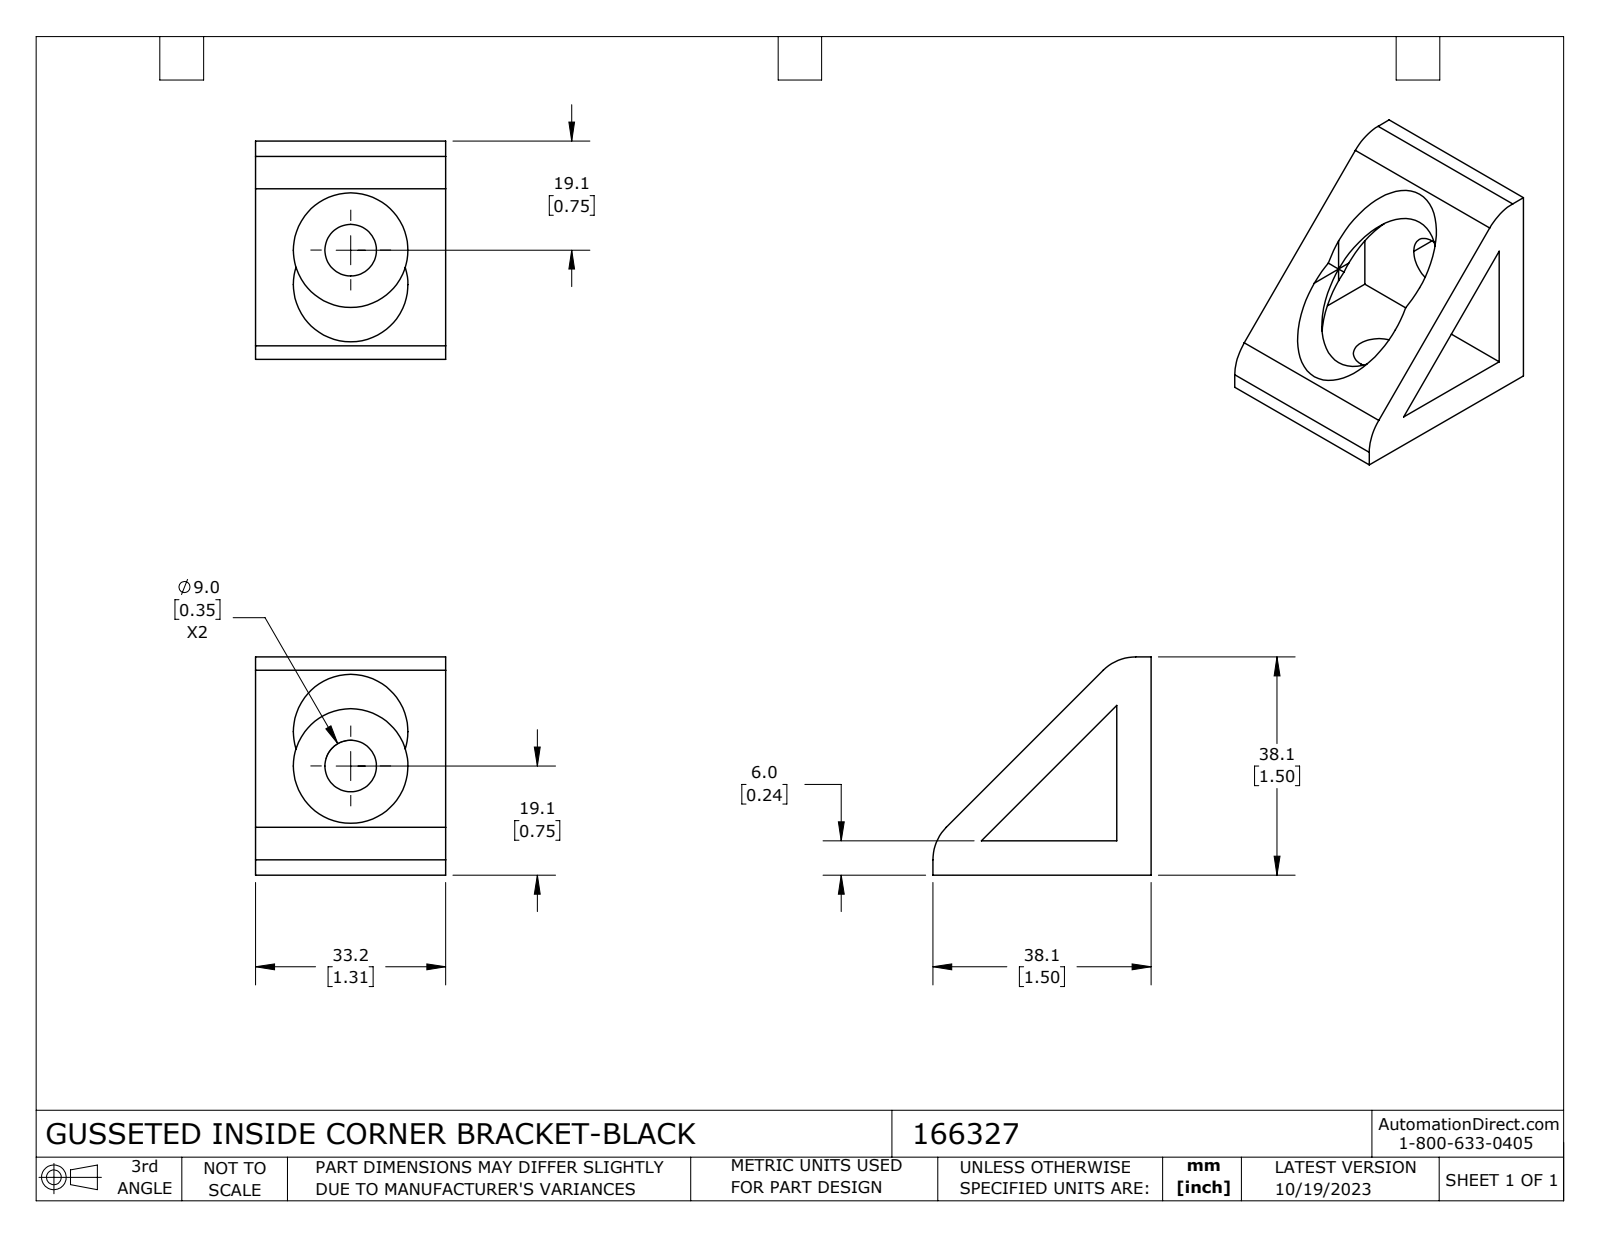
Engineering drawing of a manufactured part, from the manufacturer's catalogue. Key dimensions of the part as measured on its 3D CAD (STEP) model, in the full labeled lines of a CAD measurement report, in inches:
Part name (STEP PRODUCT): 166327
STEP written by: SolidWorks 2023 (CONFIG_CONTROL_DESIGN)
Units: inches
Bodies: 1 solid, 28 faces (10 planar, 18 cylindrical, 0 other)
Overall size (bounding box): 1.5 × 1.5 × 1.307
Volume: 1.092 in³ · Surface area: 12.3 in²
Round holes (diameter × count): ⌀0.354 ×2, ⌀0.787 ×2
Partial cylindrical surfaces — rounded edges, fillets, slot ends (radius × count): R0.315 ×2
Main face-to-face distances: 0.236, 1.307, 1.5, 1.264
